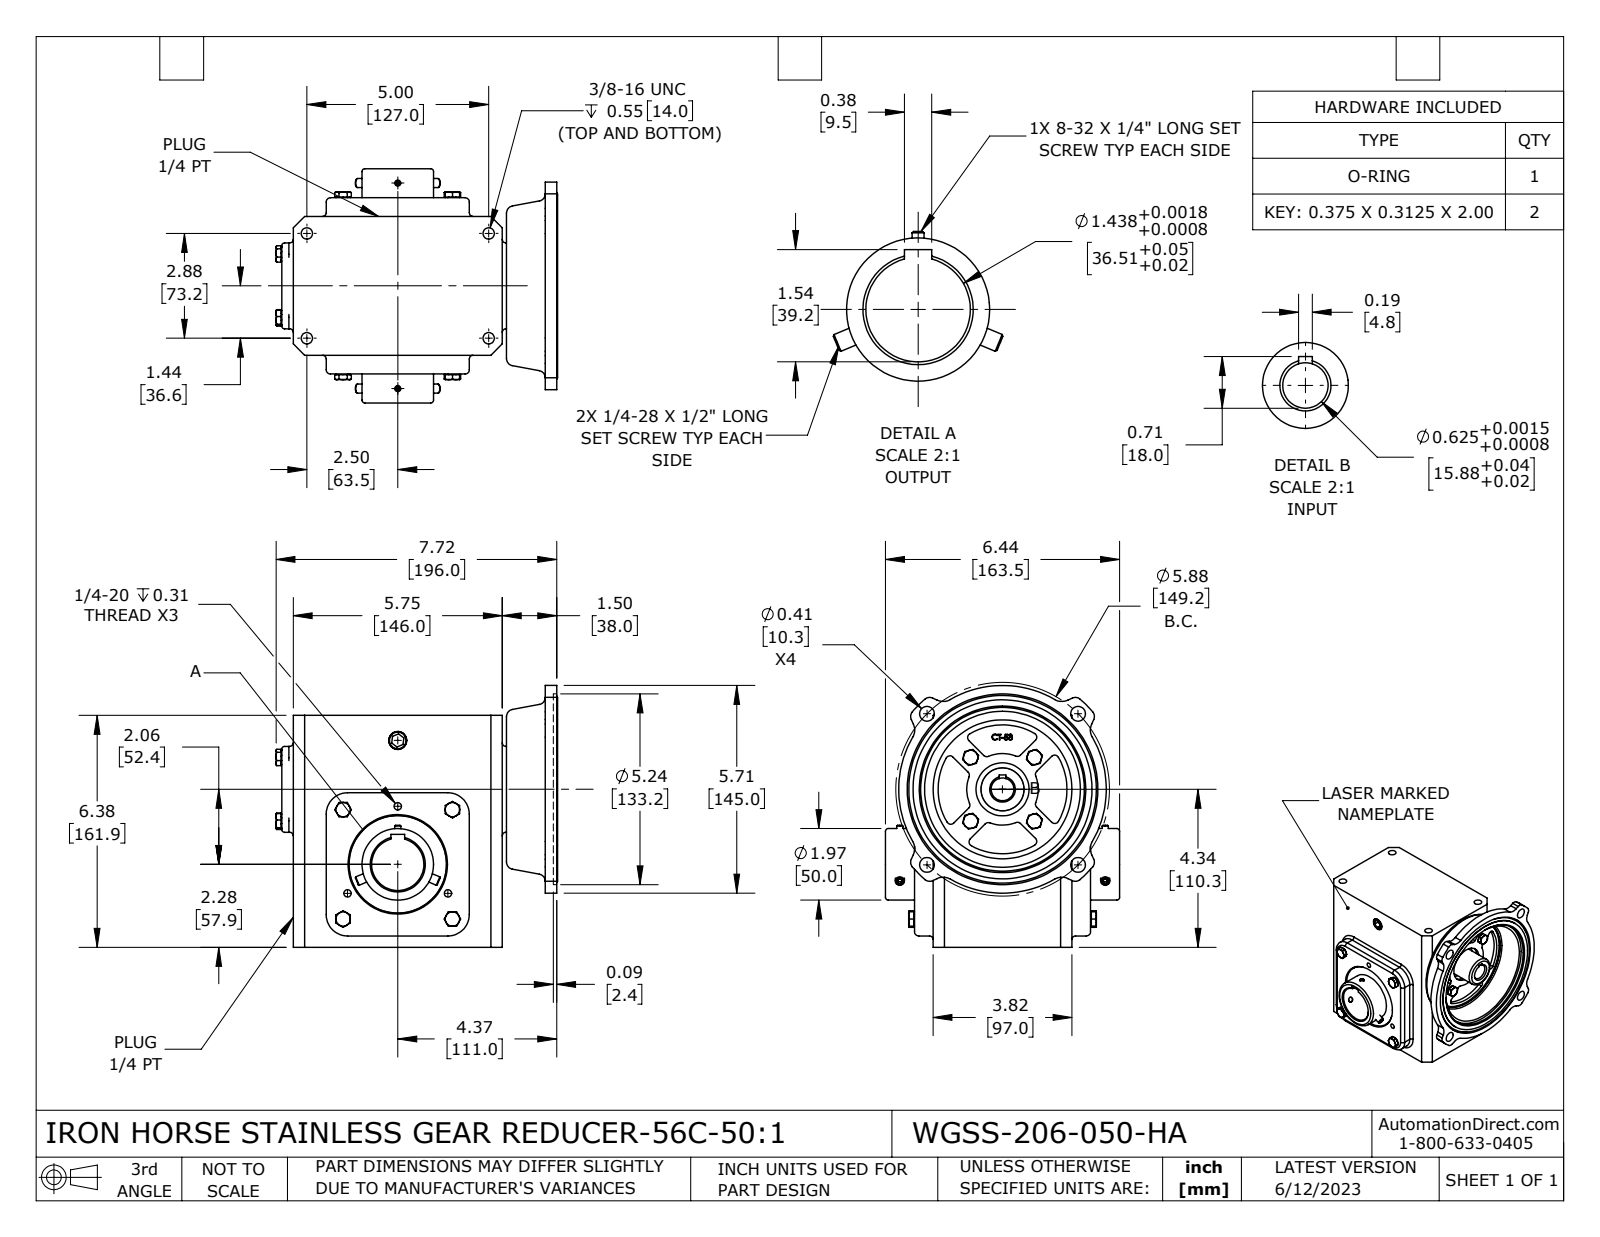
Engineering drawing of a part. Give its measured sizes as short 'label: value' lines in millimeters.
name: WGSS-206-050-HA
written by: SolidWorks 2021 (CONFIG_CONTROL_DESIGN)
unit: mm
bodies: 7 solids, 895 faces (396 planar, 235 cylindrical, 264 other)
size: 196.6 × 182.8 × 163.5
volume: 2 617 000 mm³; area: 208 800 mm²
holes: 4× ⌀5.4, 4× ⌀8, 4× ⌀10.3, 3× ⌀5.1, 2× ⌀3.5, 1× ⌀15.9, 1× ⌀22, 1× ⌀36.5, 1× ⌀36.6, 1× ⌀37, 1× ⌀40, 1× ⌀97
bosses: 8× ⌀10, 4× ⌀6.4, 2× ⌀4.2, 1× ⌀125, 1× ⌀68, 1× ⌀50, 1× ⌀30
rounds: 24× R3, 16× R2.5, 12× R10, 8× R5, 4× R2, 4× R8, 4× R15, 1× R25
face distances: 161.9, 97, 13, 110, 146, 3, 8, 184, 123, 4
hole spacings: 72.6, 74.6, 105.5, 125.6, 40.5, 143.5, 70.2, 73.2
